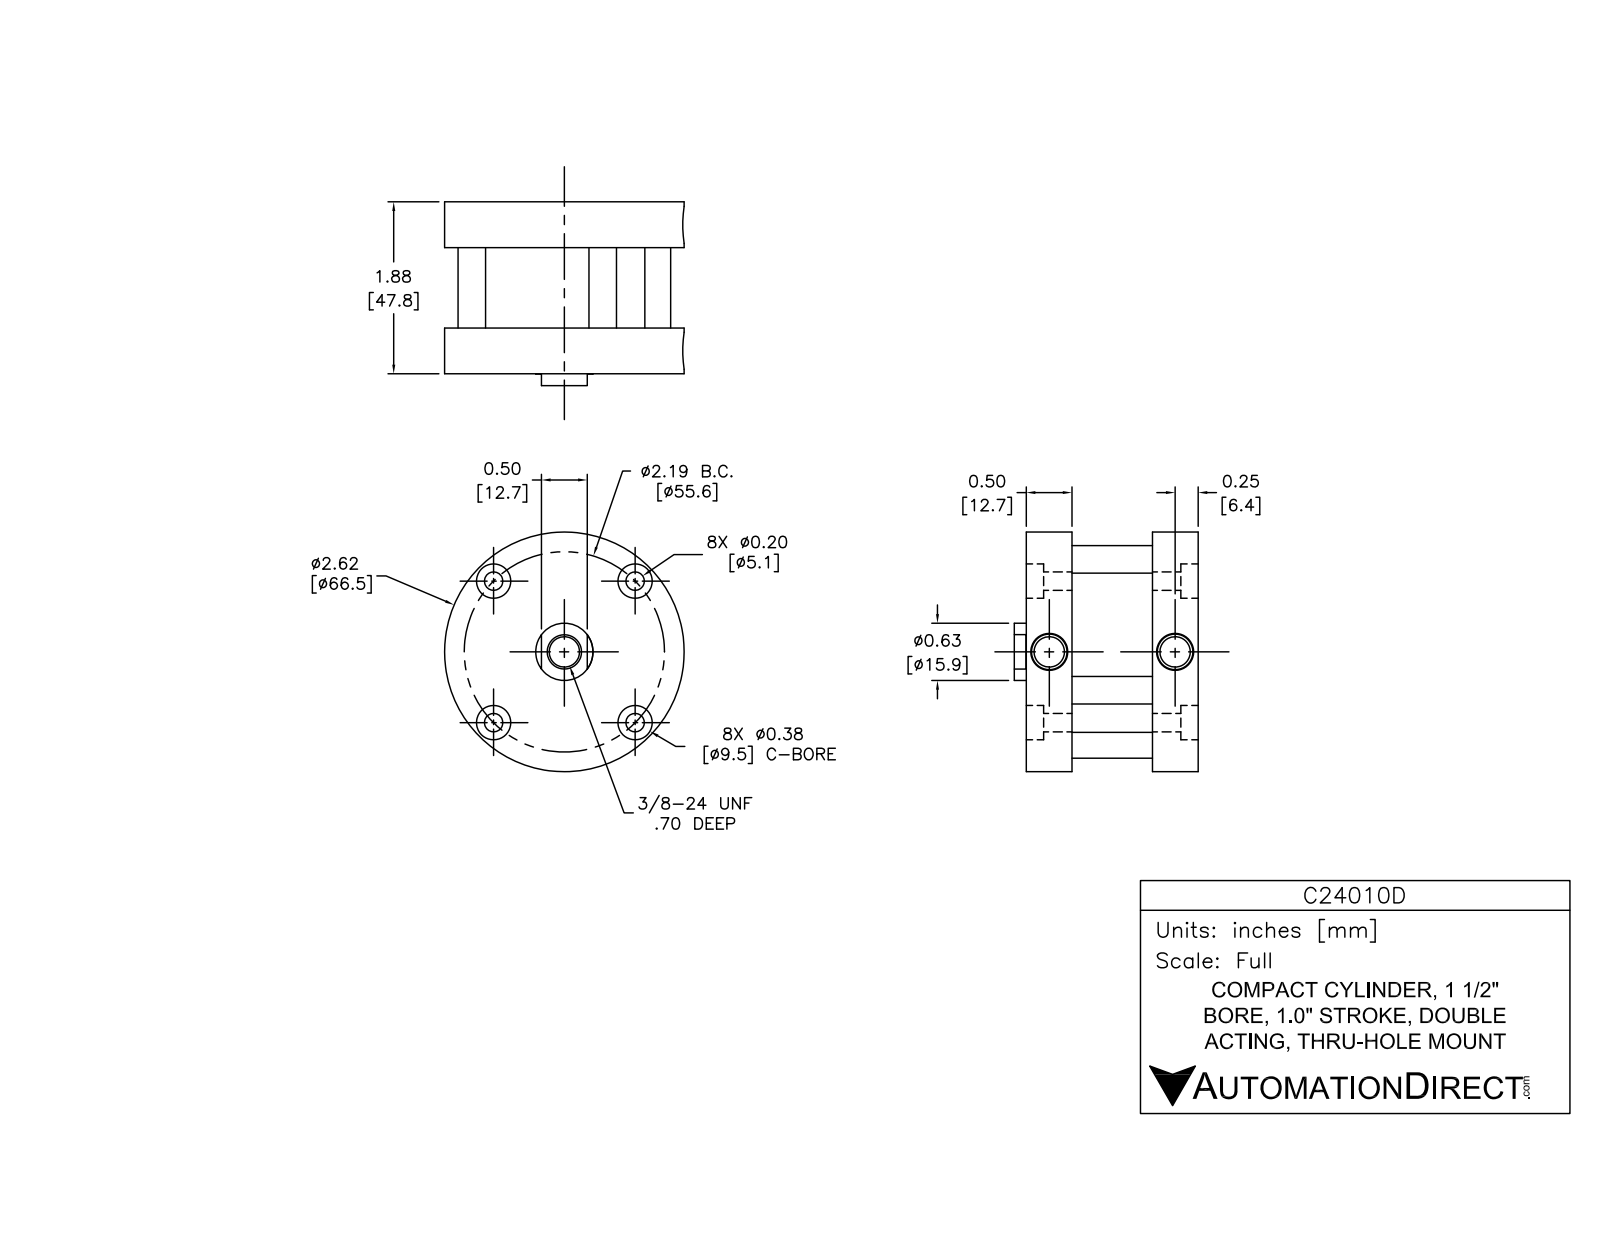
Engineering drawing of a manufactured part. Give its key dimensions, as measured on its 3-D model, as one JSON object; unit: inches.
{"part_name": "C24010D; C24010D-FO1_BM_r; C24010D-FO1_BM_heads (2); C24010D-FO1_BM_tube (+3 more)", "step_written_by": "SolidWorks 2014 (AUTOMOTIVE_DESIGN)", "units": "inches", "bodies": {"solids": 9, "faces": 165, "planar": 49, "cylindrical": 98, "other": 18}, "overall_size": [2.62, 2.62, 2.01], "volume_in3": 5.714, "surface_area_in2": 65.89, "round_holes": [[0.2, 4], [0.218, 4], [0.343, 4], [0.125, 2], [0.33, 1], [0.63, 1], [0.632, 1], [1.503, 1], [1.563, 1]], "round_bosses_or_shafts": [[0.4, 4], [2.62, 1]], "face_to_face_distances": [0.5, 1.38, 0.282, 1.598, 1.098, 0.218, 1.88, 0.88, 1.316, 0.598], "hole_center_spacings": [1.095, 1.549, 0.428, 1.217, 1.821, 2.148, 2.19, 2.191]}
